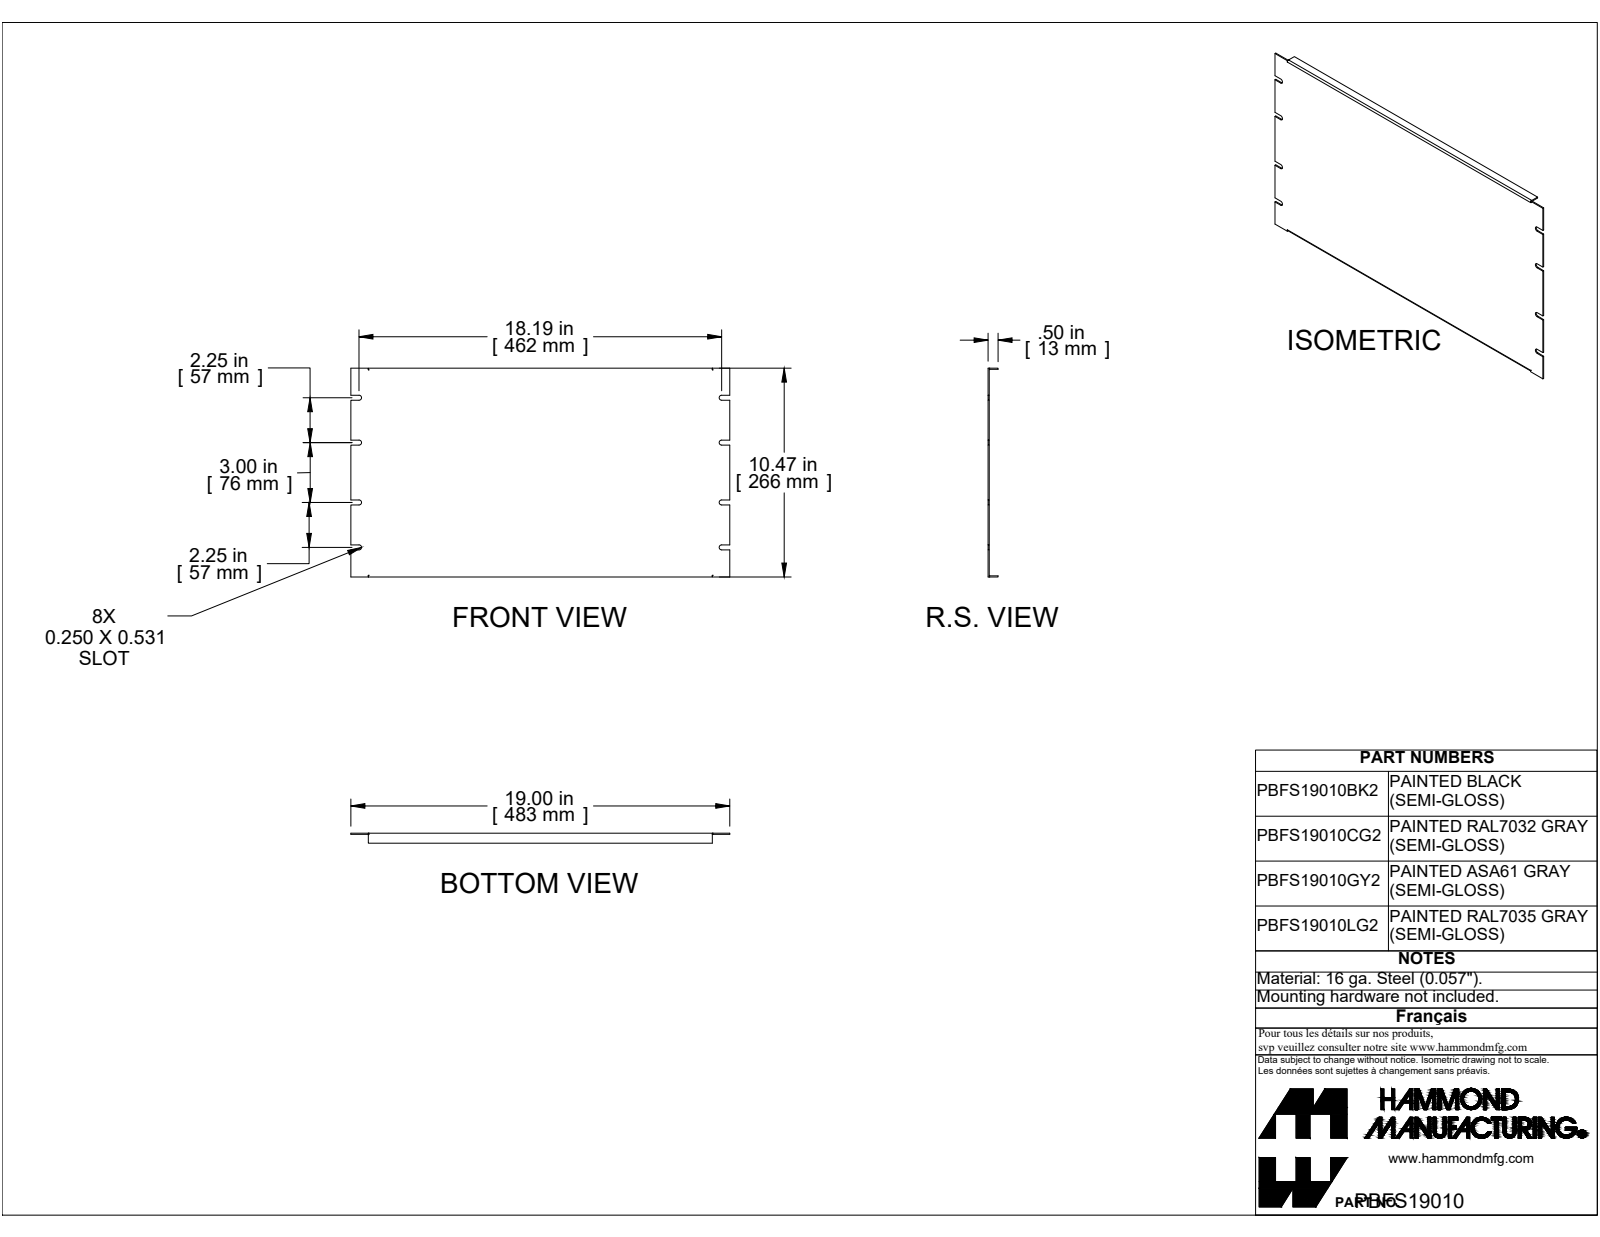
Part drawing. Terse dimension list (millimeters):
name: PBFS19010
written by: SolidWorks 2019 (CONFIG_CONTROL_DESIGN)
unit: mm
bodies: 1 solid, 62 faces (50 planar, 12 cylindrical, 0 other)
size: 482.6 × 265.9 × 12.7
volume: 198 300 mm³; area: 276 500 mm²
rounds: 8× R3.2, 2× R0.7, 2× R2.2
face distances: 1.4, 1.4, 264.4, 265.9, 263, 12.7, 11.3, 482.6, 6.4, 57.2
